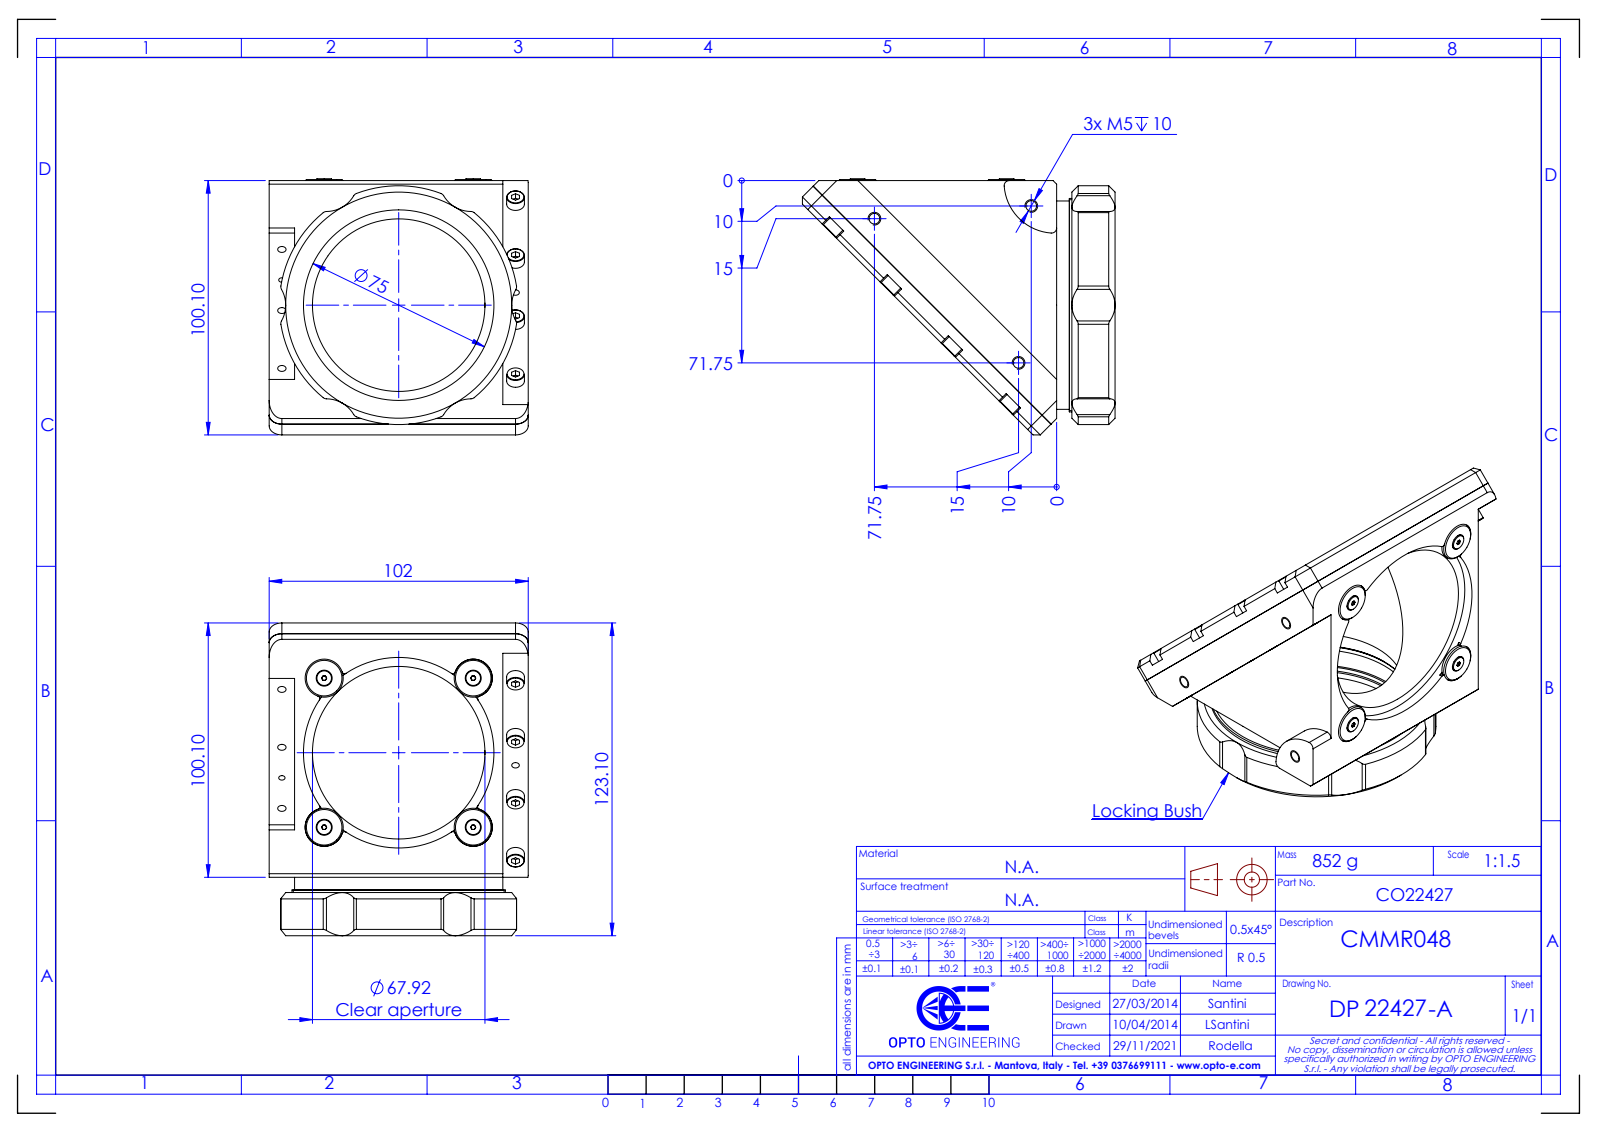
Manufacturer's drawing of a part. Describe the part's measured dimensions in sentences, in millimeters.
The part is named "DP22427 -A_CMMR048". Its 3-D file was written by "SolidWorks 2021 (CONFIG_CONTROL_DESIGN)". It is 0 solids with 382 faces: 146 planar, 154 cylindrical and 82 other. Overall it measures 123.1 by 102 by 100.83 millimeters. Round holes: 8 of diameter 3.3, 3 of diameter 4.2, 2 of diameter 3, 2 of diameter 15, 2 of diameter 67.92, 2 of diameter 75, 1 of diameter 2.5, 1 of diameter 75.6, 1 of diameter 77.2, 1 of diameter 79, 1 of diameter 82, 1 of diameter 84. Round bosses or shafts: 8 of diameter 7, 4 of diameter 5.75, 2 of diameter 15. Partial cylindrical surfaces (rounded edges, fillets, slot ends): 14 of radius 2, 8 of radius 1, 6 of radius 12.5, 4 of radius 4, 4 of radius 5, 4 of radius 25, 1 of radius 20, 1 of radius 47. The main face-to-face distances are 8, 10, 92, 82, 7, 3.8, 11.8, 15, 23, 102. The hole center spacings are 92, 17, 93.56, 97.48, 104.34, 32.22, 32.23, 34.
